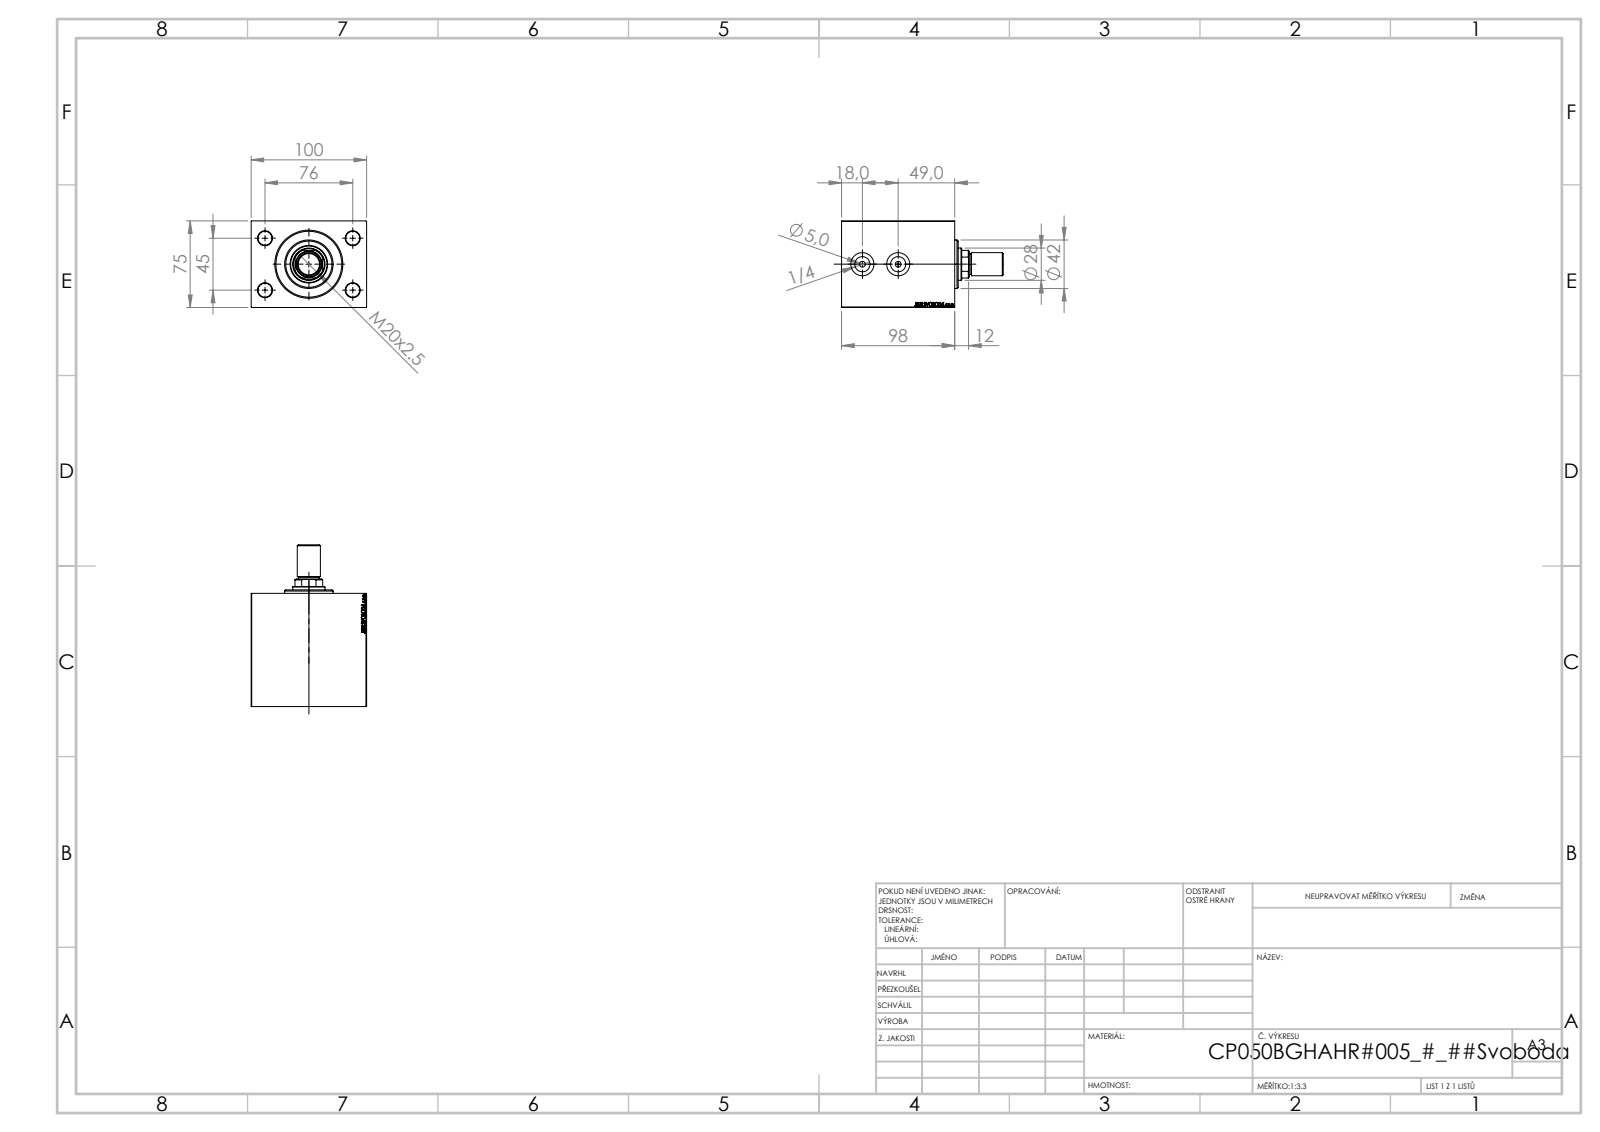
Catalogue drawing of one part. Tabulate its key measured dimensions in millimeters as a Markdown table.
| quantity | value |
| --- | --- |
| part name | V450CP_B_VCP; V450CP_VC_B; V450CM_MALE_METRIC; V450CP_B |
| STEP written by | SolidWorks 2019 (CONFIG_CONTROL_DESIGN) |
| units | millimeters |
| bodies | 4 solids, 918 faces (410 planar, 72 cylindrical, 436 other) |
| overall size | 140 × 100 × 75 |
| volume | 714 384 mm³ |
| surface area | 106 349 mm² |
| round holes (diameter × count) | 12 × 4, 4 × 2, 5 × 2, 9.73 × 2, 13.16 × 2, 15 × 2, 20 × 2, 18.5 × 1, 28 × 1, 31.5 × 1, 32.5 × 1, 50 × 1 |
| round bosses / shafts (diameter × count) | 42 × 1, 20 × 1, 18 × 1 |
| partial cylindrical surfaces (radius × count) | 13.5 × 1 |
| main face-to-face distances | 75, 100, 98, 49, 14, 84, 44, 5, 35, 30 |
| hole center spacings | 44.16, 45, 76, 88.32, 31, 42.55 |
